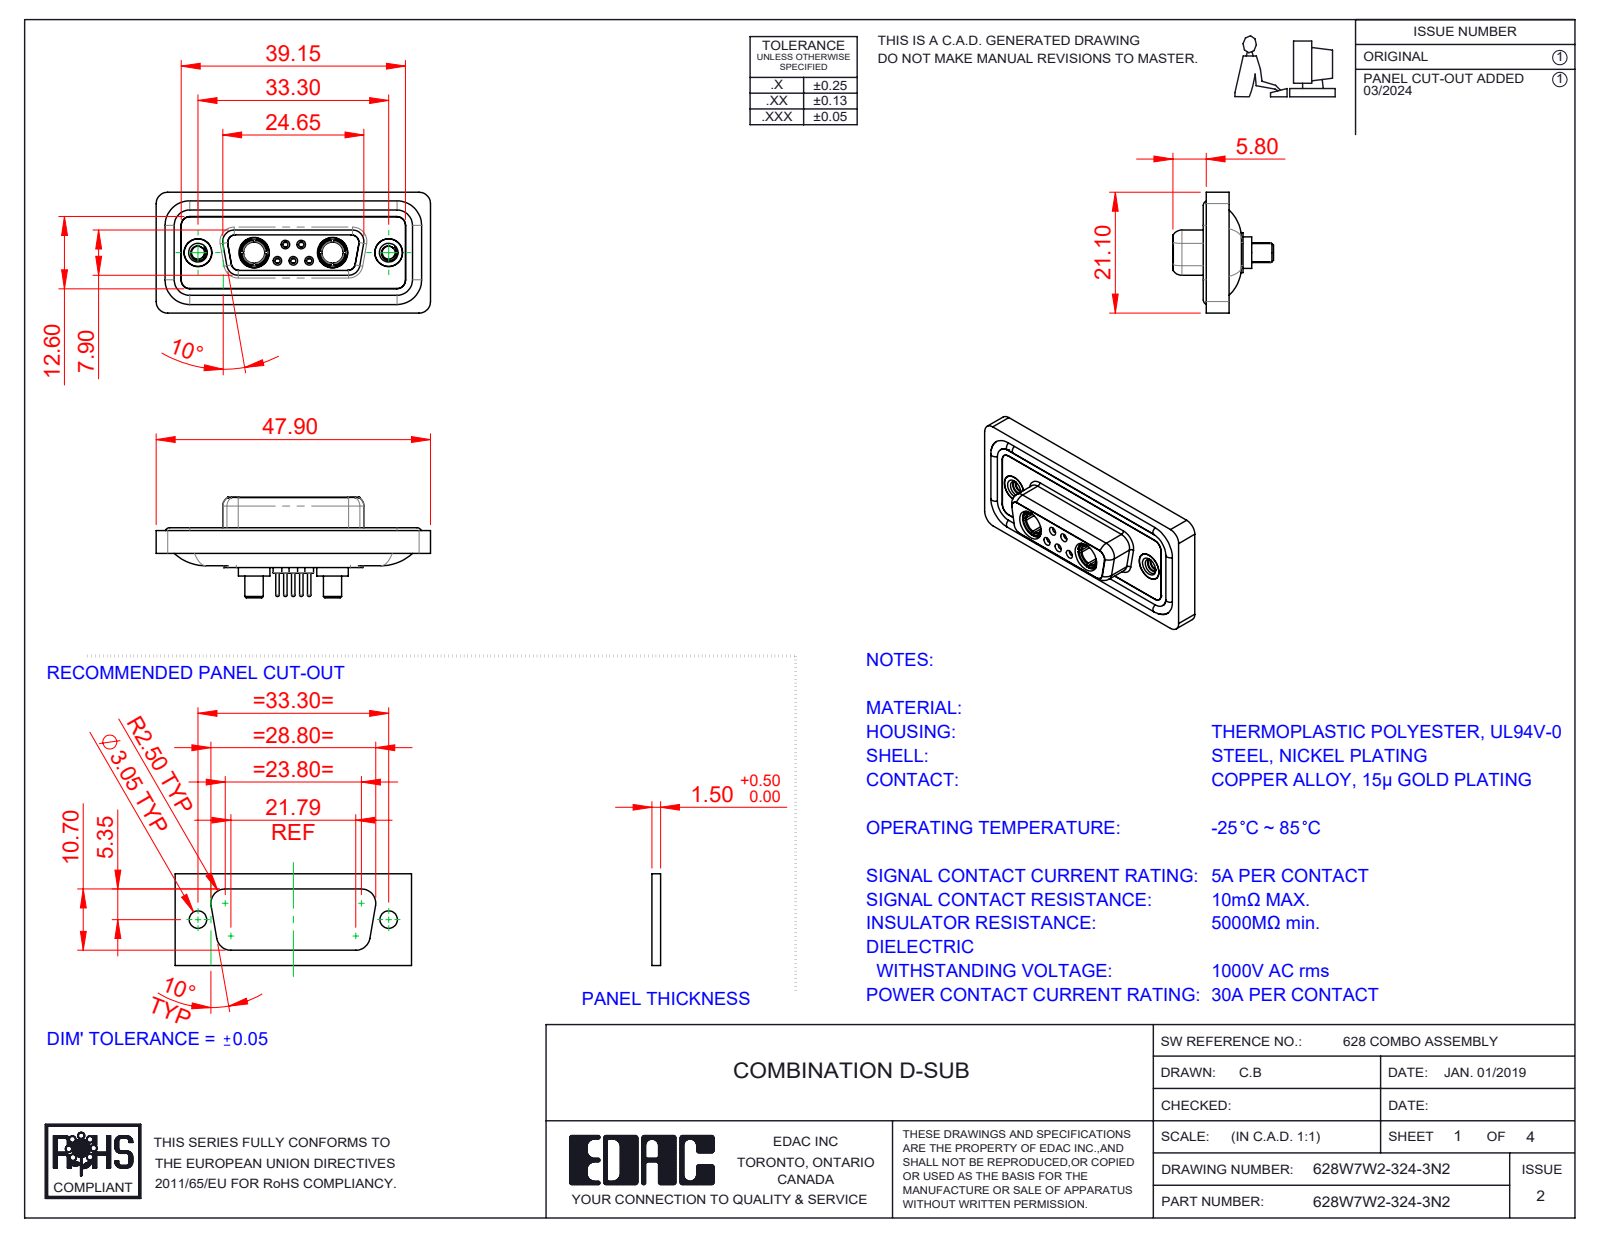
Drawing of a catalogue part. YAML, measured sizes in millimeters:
part_name: "628Combo Housing_7W2; 628Combo Waterproof Housing_15 Contacts; 628W7W2-324-3N2; 628Combo Contact Row 1_24 (+5 more)"
step_written_by: "SolidWorks 2023 (CONFIG_CONTROL_DESIGN)"
units: millimeters
bodies: {solids: 16, faces: 809, planar: 238, cylindrical: 329, other: 242}
overall_size: [47.9, 21.1, 17.55]
volume: 6091
surface_area: 9894
round_holes:
  - {diameter: 0.9, count: 5}
  - {diameter: 1.1, count: 5}
  - {diameter: 1.5, count: 5}
  - {diameter: 2, count: 5}
  - {diameter: 4.85, count: 4}
  - {diameter: 1.6, count: 3}
  - {diameter: 1.7, count: 2}
  - {diameter: 2.26, count: 2}
  - {diameter: 3.7, count: 2}
  - {diameter: 4, count: 2}
  - {diameter: 4.05, count: 2}
  - {diameter: 5, count: 2}
round_bosses_or_shafts:
  - {diameter: 1.6, count: 6}
  - {diameter: 2.2, count: 5}
  - {diameter: 0.6, count: 5}
  - {diameter: 5.5, count: 2}
  - {diameter: 5.2, count: 2}
  - {diameter: 4.96, count: 2}
  - {diameter: 4.95, count: 2}
  - {diameter: 4.8, count: 2}
partial_cylinders:
  - {radius: 1.5, count: 22}
  - {radius: 2, count: 20}
  - {radius: 1.35, count: 12}
  - {radius: 1.6, count: 8}
  - {radius: 0.25, count: 4}
  - {radius: 0.5, count: 4}
  - {radius: 0.6, count: 4}
  - {radius: 0.65, count: 4}
face_to_face_distances: [0.4, 1.8, 1.6, 0.5, 2.9, 7.45, 1.1, 5.65, 6.6, 7.05]
hole_center_spacings: [3.16, 2.77, 9.8, 23.5, 4.31, 4.33, 5.03, 5.04]
